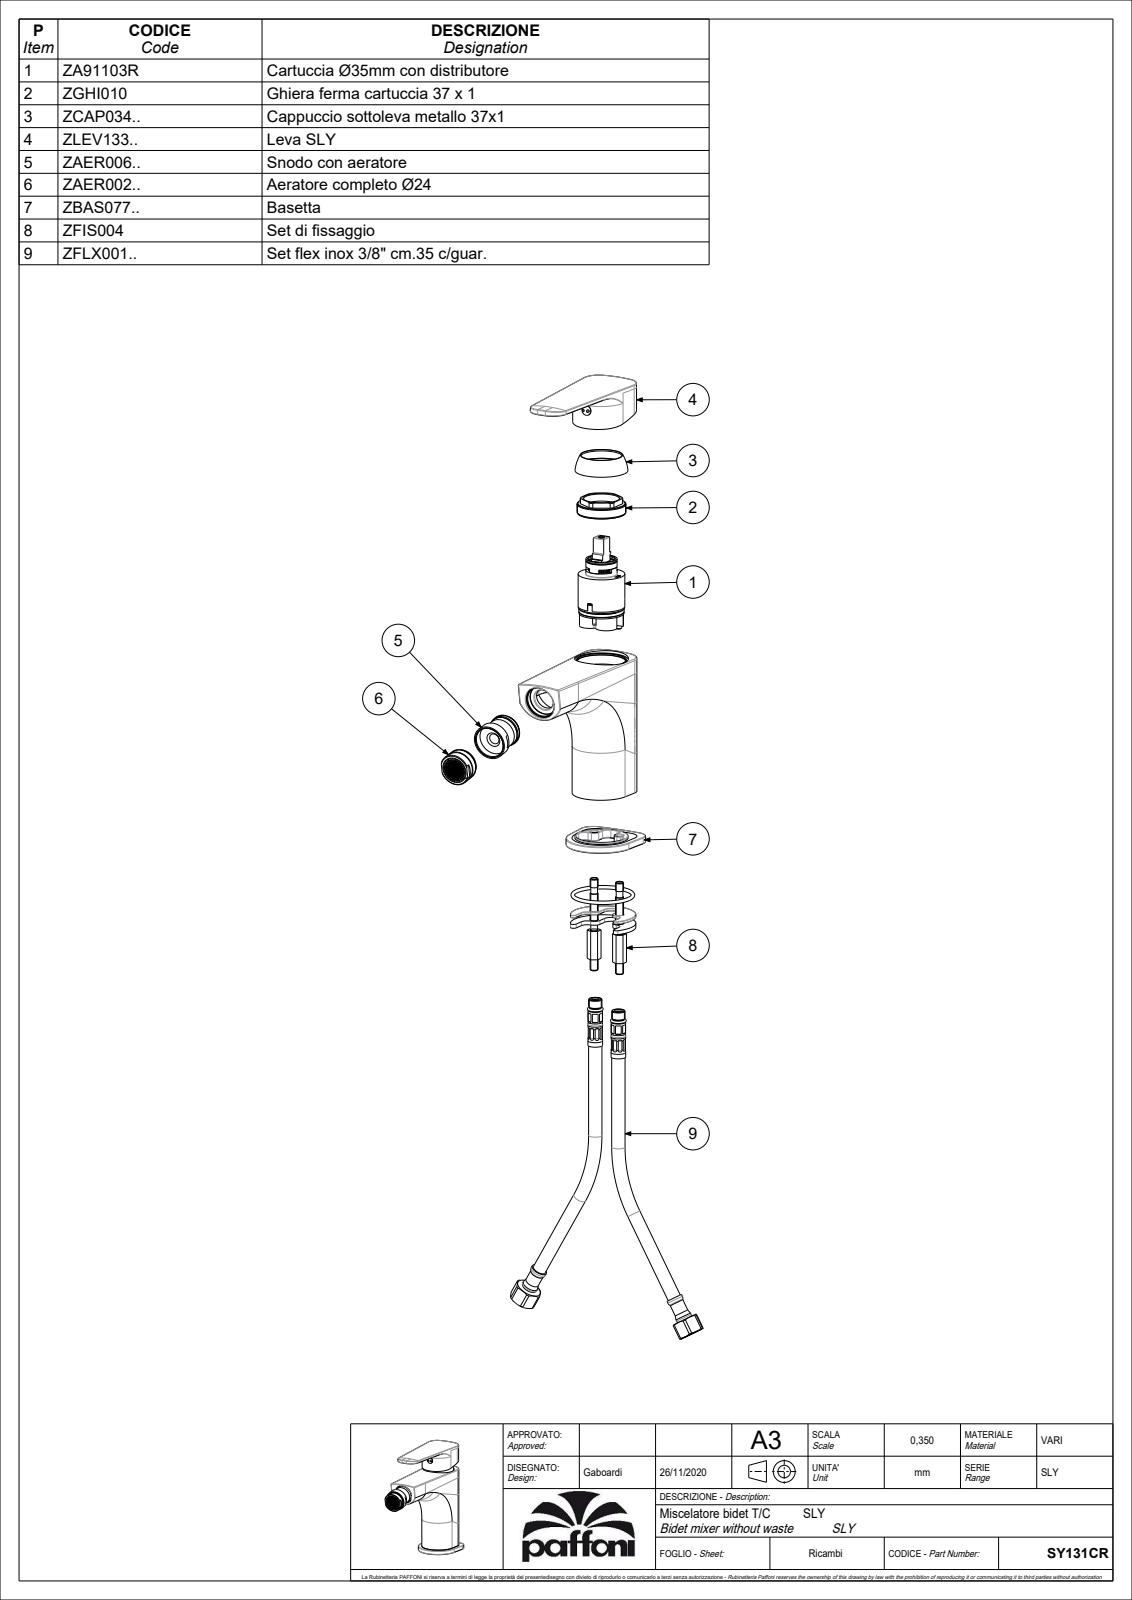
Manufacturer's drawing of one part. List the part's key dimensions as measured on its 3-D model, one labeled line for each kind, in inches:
Part name (STEP PRODUCT): SY131CR
STEP written by: CREO PARAMETRIC BY PTC INC, 2020044 (CONFIG_CONTROL_DESIGN)
Units: inches
Bodies: 2 solids, 2873 faces (2109 planar, 396 cylindrical, 368 other)
Overall size (bounding box): 5.917 × 5.583 × 2.119
Volume: 10.37 in³ · Surface area: 168.7 in²
Round holes (diameter × count): ⌀0.354 ×5, ⌀0.315 ×3, ⌀0.472 ×3, ⌀0.157 ×2, ⌀0.181 ×2, ⌀0.217 ×2, ⌀0.244 ×2, ⌀0.276 ×2, ⌀0.433 ×2, ⌀0.63 ×2, ⌀0.118 ×1, ⌀0.13 ×1
Round bosses / shafts (diameter × count): ⌀0.394 ×3, ⌀0.197 ×3, ⌀0.425 ×2, ⌀0.323 ×2, ⌀0.236 ×2, ⌀1.654 ×1, ⌀1.575 ×1, ⌀1.378 ×1
Partial cylindrical surfaces — rounded edges, fillets, slot ends (radius × count): R0.02 ×55, R0.006 ×11, R0.059 ×10, R0.012 ×9, R0.039 ×4, R0.197 ×4, R0.276 ×4, R0.394 ×4
Main face-to-face distances: 0.118, 0.197, 0.374, 2.323, 0.591, 0.236, 0.335, 0.079, 0.846, 0.256
Hole centre spacings: 0.535, 0.02, 0.028, 0.044, 0.335, 0.339, 0.355, 0.44
